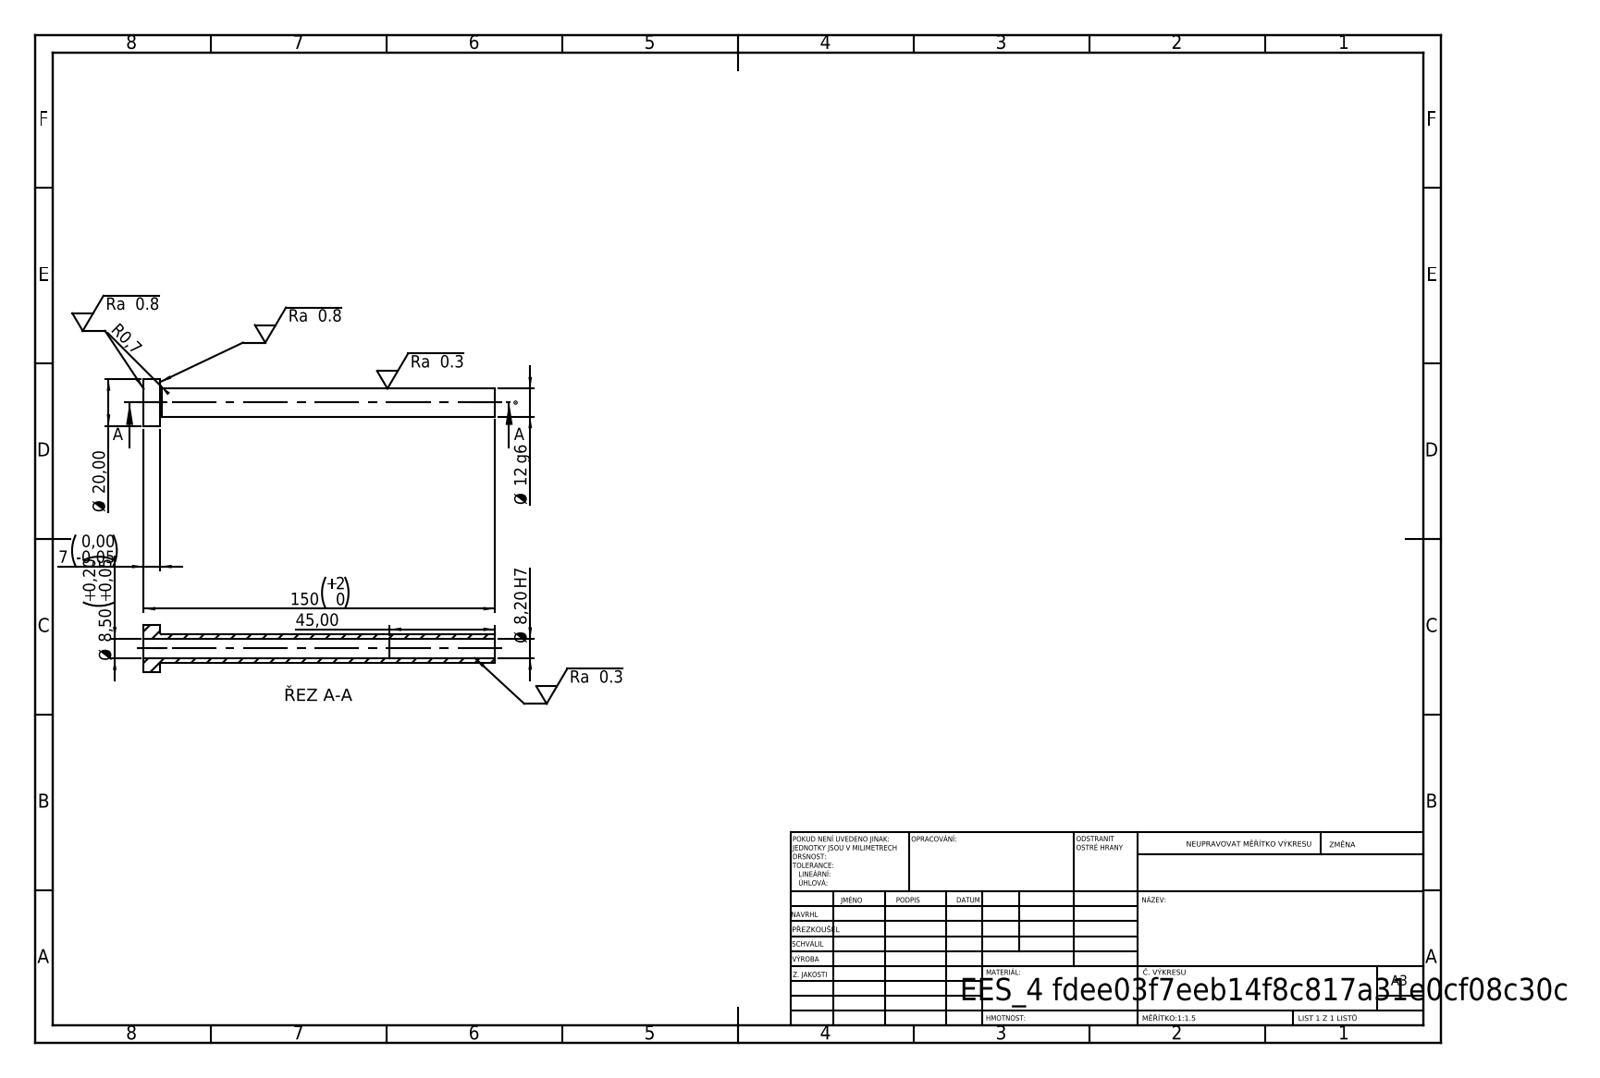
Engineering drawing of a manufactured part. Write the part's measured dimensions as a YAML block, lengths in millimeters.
step_written_by: "SolidWorks 2019 (CONFIG_CONTROL_DESIGN)"
units: millimeters
bodies: {solids: 1, faces: 14, planar: 4, cylindrical: 8, other: 2}
overall_size: [150, 20, 20]
volume: 10041
surface_area: 10306
round_holes:
  - {diameter: 8.2, count: 1}
  - {diameter: 8.5, count: 1}
round_bosses_or_shafts:
  - {diameter: 20, count: 1}
  - {diameter: 12, count: 1}
face_to_face_distances: [7, 150, 143, 105, 98, 45]
